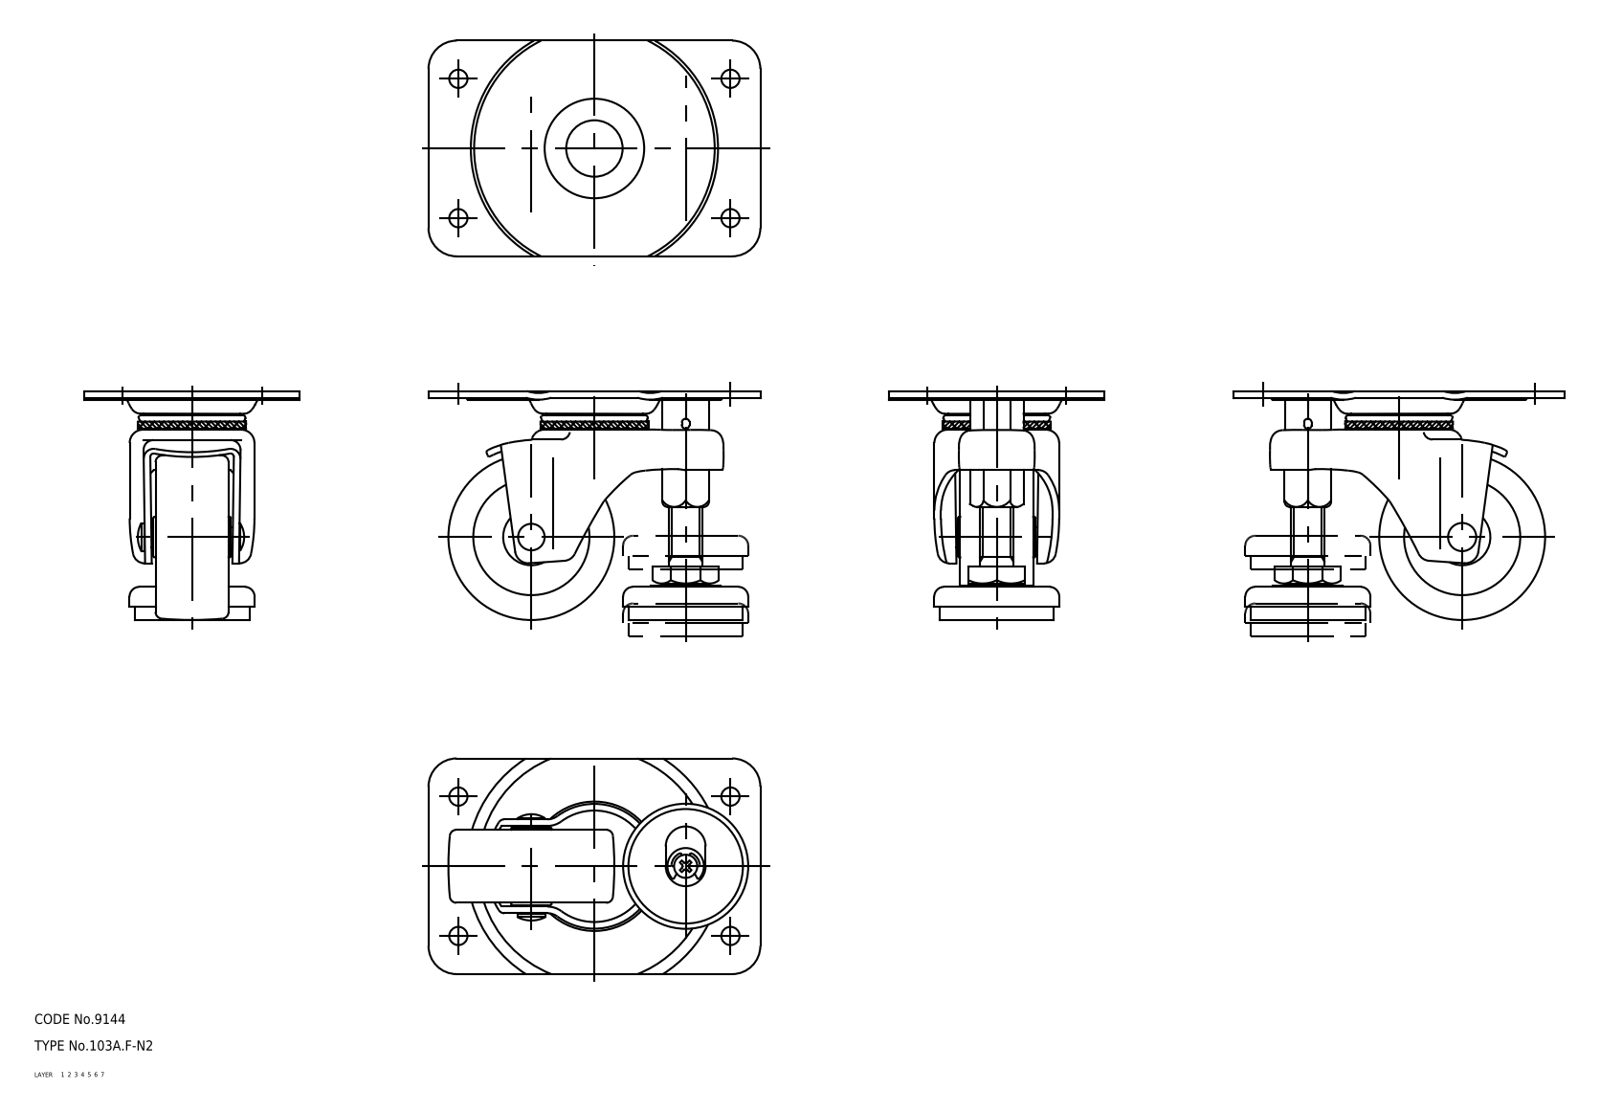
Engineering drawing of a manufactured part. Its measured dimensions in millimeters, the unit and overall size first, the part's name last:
Units: millimetres
Overall size (bounding box): 100 × 69 × 65
Volume: 81 162 mm³ · Surface area: 42 384 mm²
Bodies: 6 solids, 338 faces (0 planar, 0 cylindrical, 338 other)
Part name (STEP PRODUCT): wheel; mounting plate; main shaft; foot (+2 more)
STEP written by: CADfix (AUTOMOTIVE_DESIGN)
